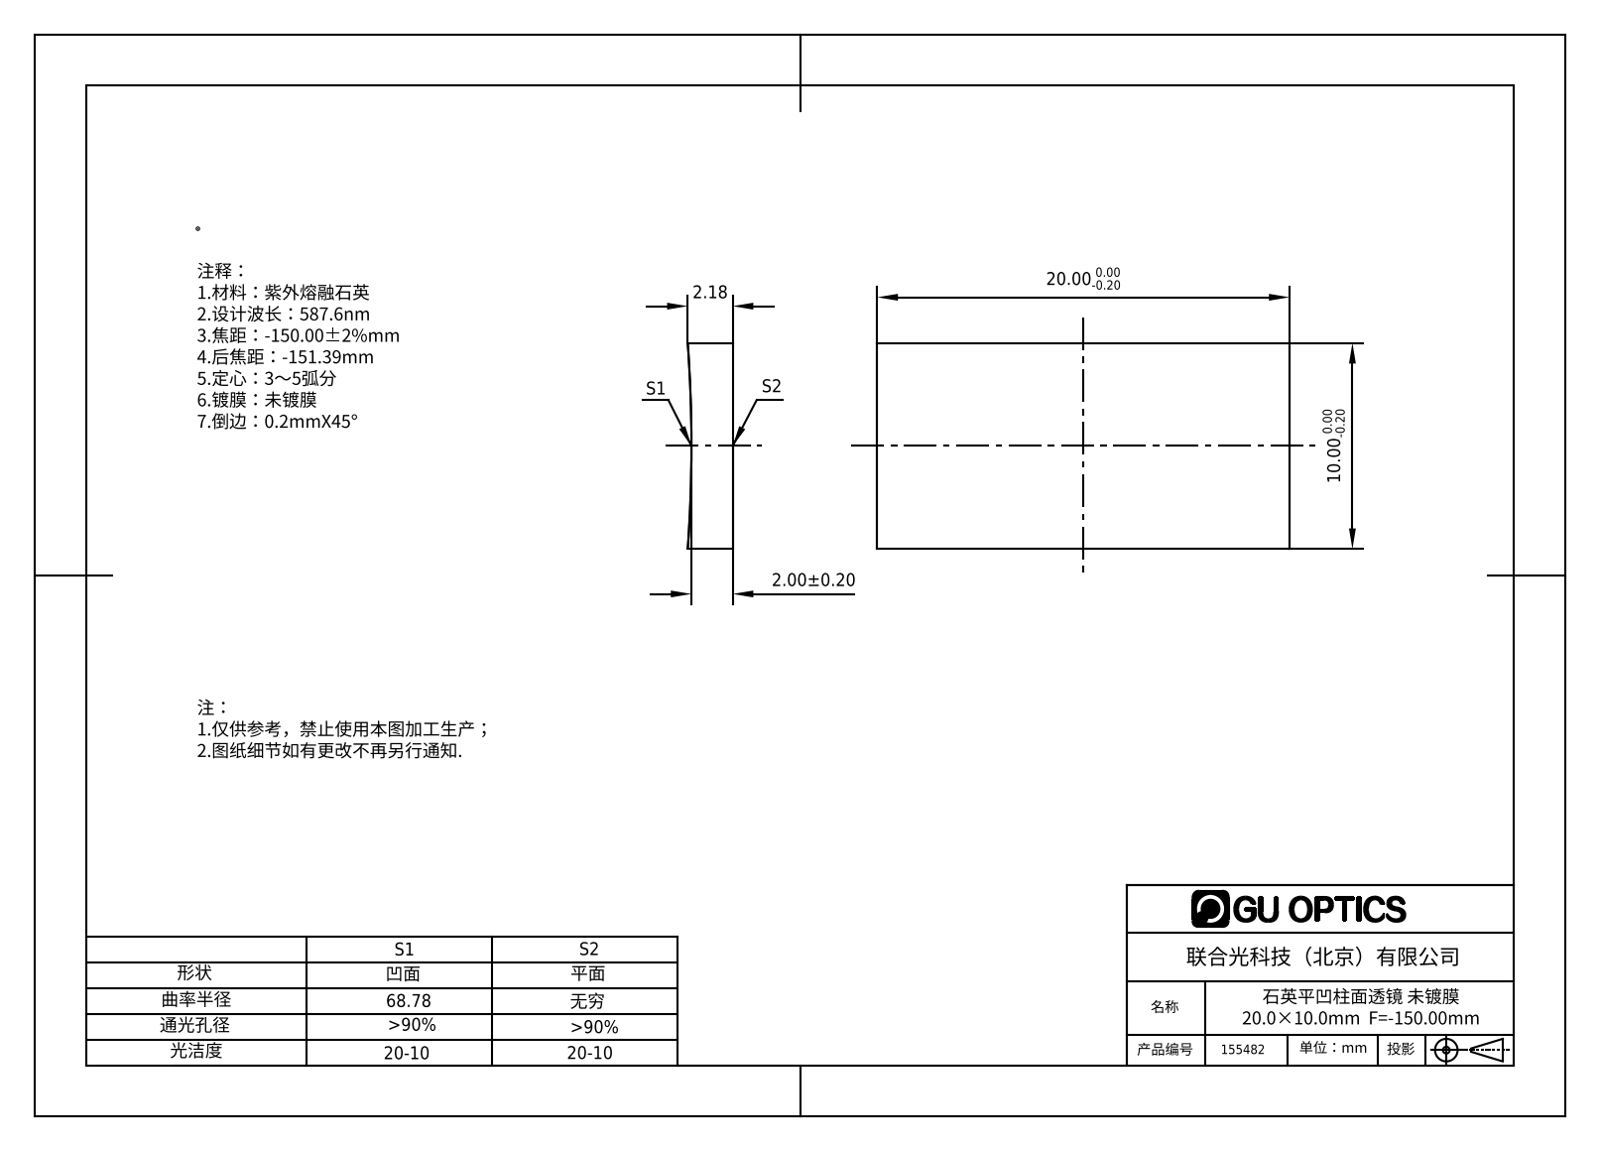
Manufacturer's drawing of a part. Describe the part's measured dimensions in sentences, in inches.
The part is named "155482". Its 3-D file was written by "SolidWorks 2016 (AUTOMOTIVE_DESIGN)". It is 1 solid with 6 faces: 5 planar, 1 cylindrical and 0 other. Overall it measures 0.787 by 0.394 by 0.086 inches. Its volume is 0.025 cubic inches and its surface area 0.82 square inches. Partial cylindrical surfaces (rounded edges, fillets, slot ends): 1 of radius 2.708. The main face-to-face distances are 0.394, 0.787.
